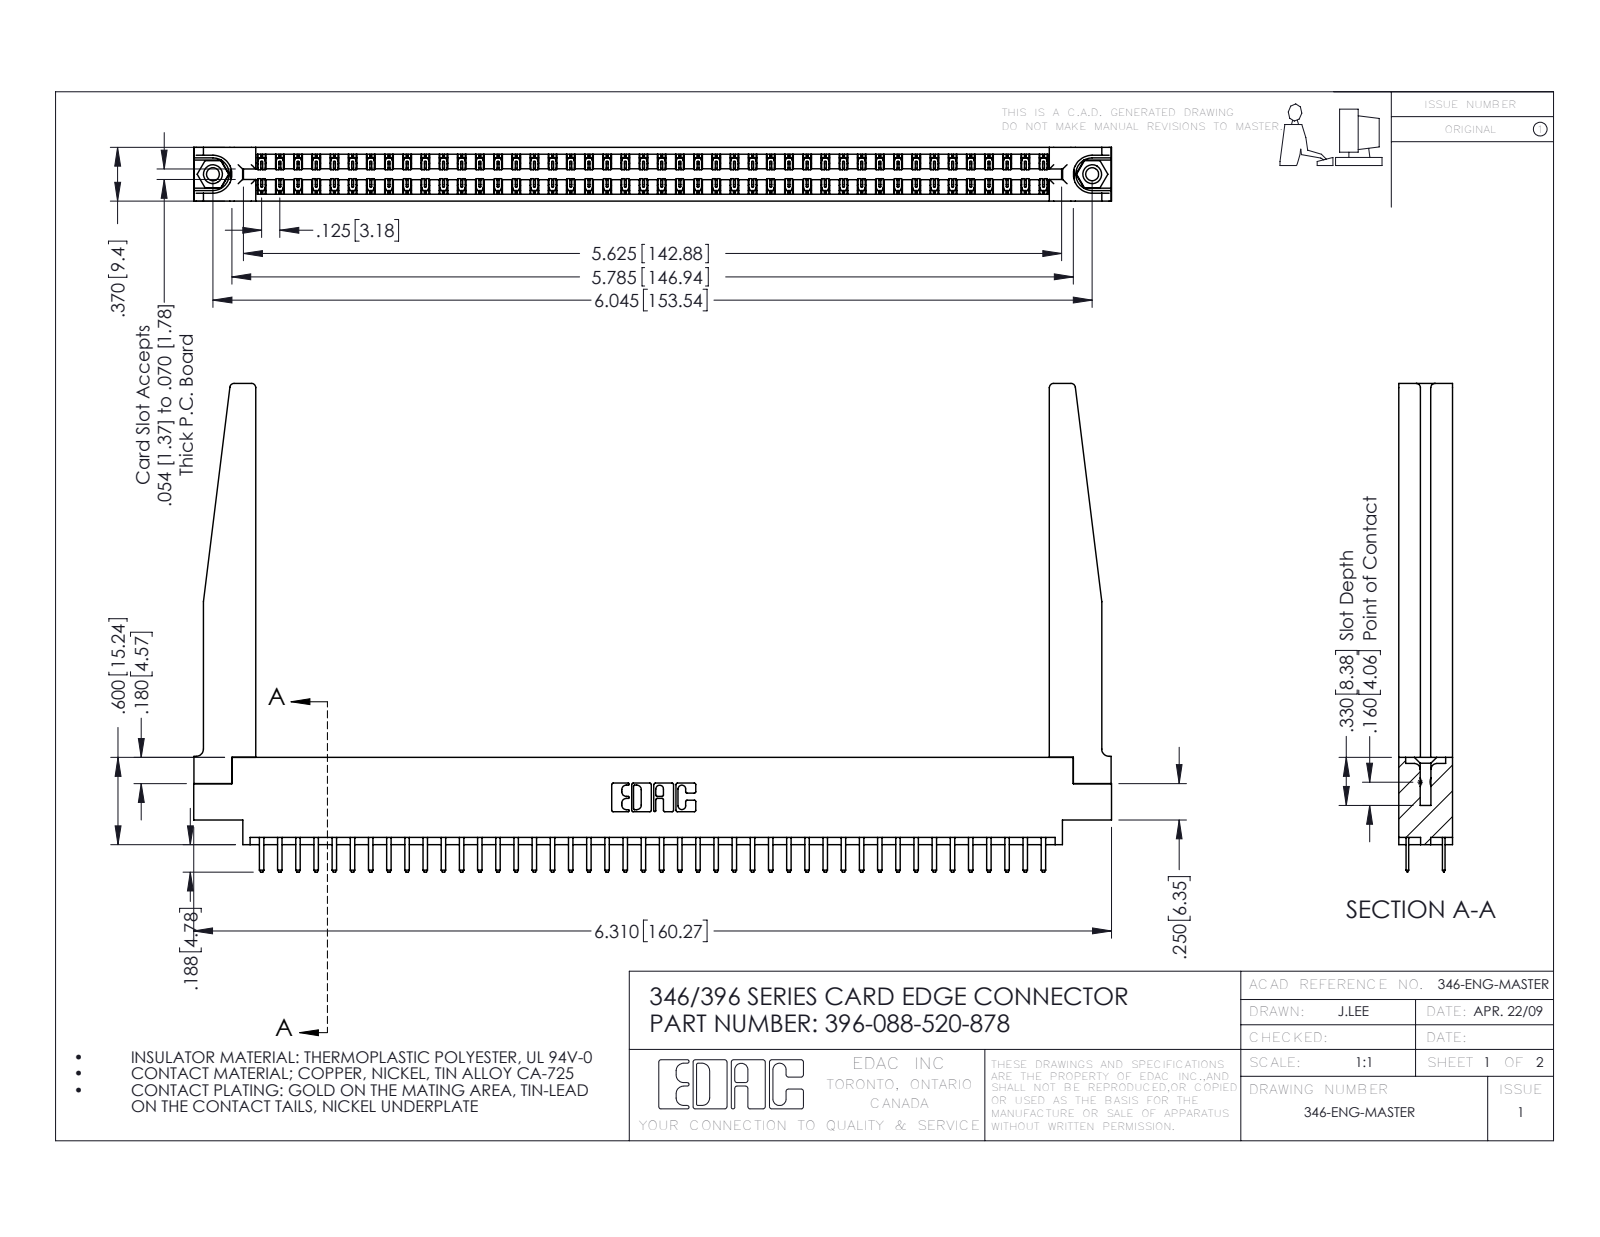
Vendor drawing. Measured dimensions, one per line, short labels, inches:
name: 345-250-001_345-250-001-102; 346 Part_0.170 Offset - 0.156 Dia-TH; 345-292-001_345-293-120; 396-088-520-878 (+1 more)
written by: SolidWorks 2016 (CONFIG_CONTROL_DESIGN)
unit: in
bodies: 93 solids, 5288 faces (3478 planar, 1758 cylindrical, 52 other)
size: 6.31 × 3.358 × 0.37
volume: 1.364 in³; area: 43.24 in²
holes: 2× ⌀0.089, 2× ⌀0.125, 2× ⌀0.156, 1× ⌀0.064
bosses: 2× ⌀0.155
rounds: 132× R0.006, 92× R0.01, 22× R0.01, 8× R0.03, 6× R0.007, 6× R0.031, 3× R0.026, 2× R0.014
face distances: 0.37, 0.048, 0.322, 0.25, 0.072, 0.148, 0.15, 0.298, 0.025, 0.275
hole spacings: 0.246, 5.836, 6.045
